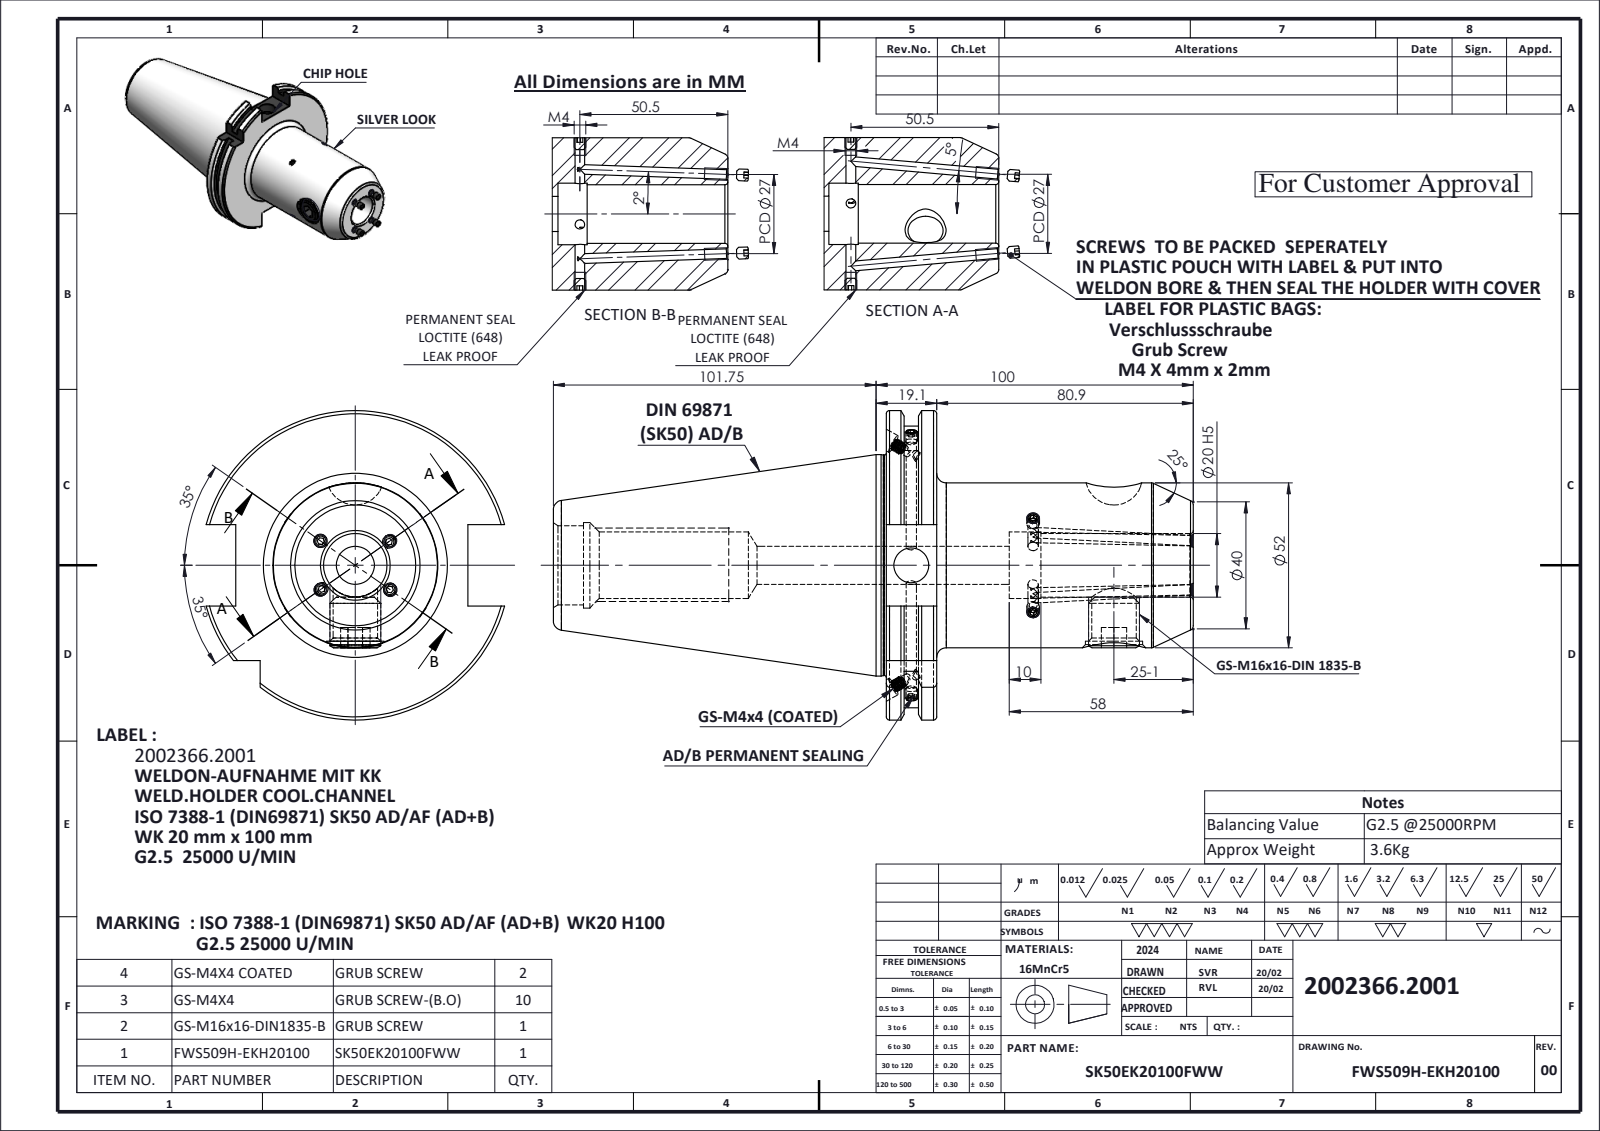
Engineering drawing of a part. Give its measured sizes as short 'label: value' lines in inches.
name: GS-M16X16-DIN1835-B_ISO 4026 - M16 x 10-N; GS-M4X4-COATING_DIN 913 - M4 x 4-N; GS-M4X4_DIN 913 - M4 x 4-N; SK50EK20100FWW (+1 more)
written by: SolidWorks 2024 (CONFIG_CONTROL_DESIGN)
unit: in
bodies: 14 solids, 438 faces (145 planar, 125 cylindrical, 168 other)
size: 8.224 × 3.839 × 3.703
volume: 28.92 in³; area: 101.6 in²
holes: 9× ⌀0.13, 2× ⌀0.126, 2× ⌀0.236, 1× ⌀0.433, 1× ⌀0.472, 1× ⌀0.551, 1× ⌀0.709, 1× ⌀0.787, 1× ⌀0.827, 1× ⌀0.984, 1× ⌀1.063
bosses: 12× ⌀0.157, 2× ⌀0.114, 1× ⌀2.75, 1× ⌀2.734, 1× ⌀2.047, 1× ⌀0.63
rounds: 1× R1.768, 1× R1.919
face distances: 0.626, 3.811, 3.185, 0.223, 0.403, 3.588, 0.4, 0.177, 0.226, 3.411
